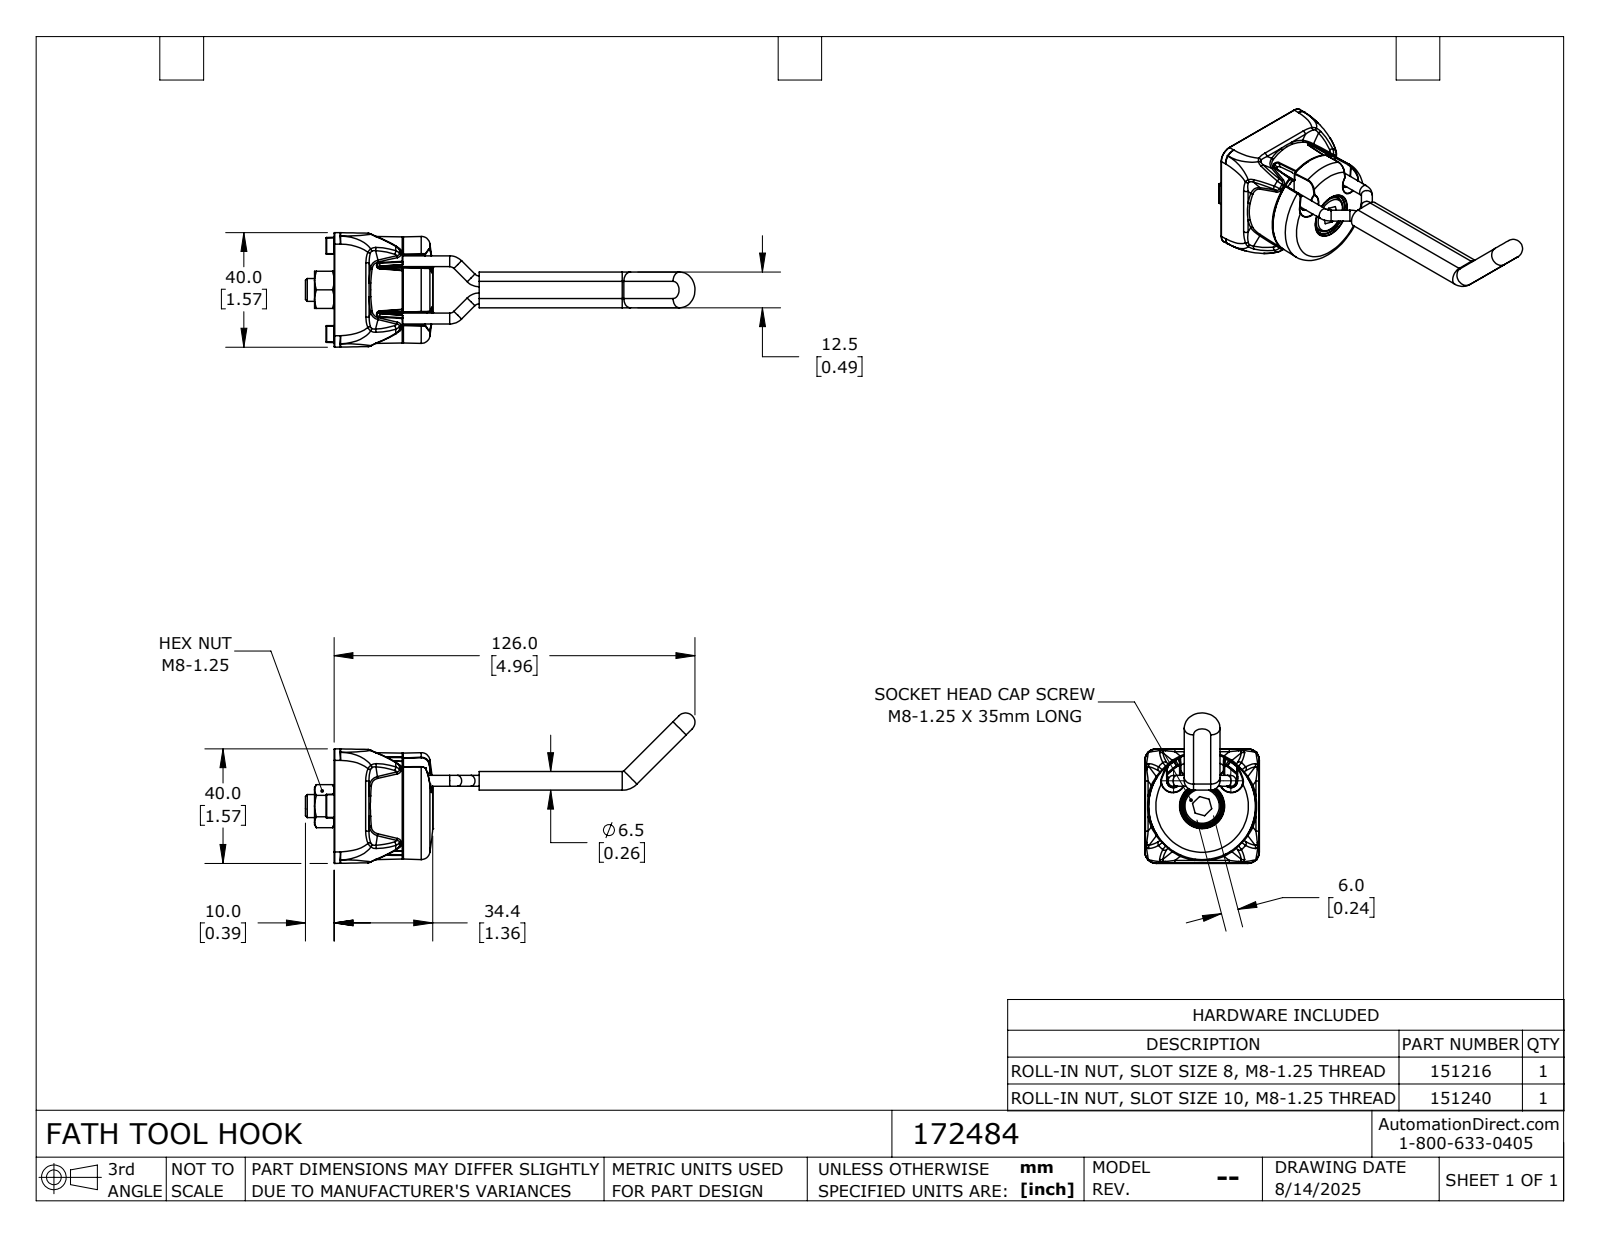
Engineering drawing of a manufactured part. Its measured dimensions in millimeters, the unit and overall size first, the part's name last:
Units: millimetres
Overall size (bounding box): 136.03 × 52.51 × 40
Round holes (diameter × count): ⌀6.8 ×1, ⌀8 ×1, ⌀13.01 ×1
Round bosses / shafts (diameter × count): ⌀3.8 ×8, ⌀13 ×1
Partial cylindrical surfaces — rounded edges, fillets, slot ends (radius × count): R0.2 ×140, R0.5 ×18, R1 ×8, R4 ×8, R1.2 ×4, R3.25 ×4, R2.15 ×2, R0.75 ×1
Main face-to-face distances: 13.5, 6.5, 13.8, 30.8, 8, 6, 17, 24, 10.5, 10.2
Volume: 44 910 mm³ · Surface area: 23 195 mm²
Bodies: 7 solids, 1212 faces (217 planar, 301 cylindrical, 694 other)
Part name (STEP PRODUCT): 172484
STEP written by: SolidWorks 2024 (CONFIG_CONTROL_DESIGN)
